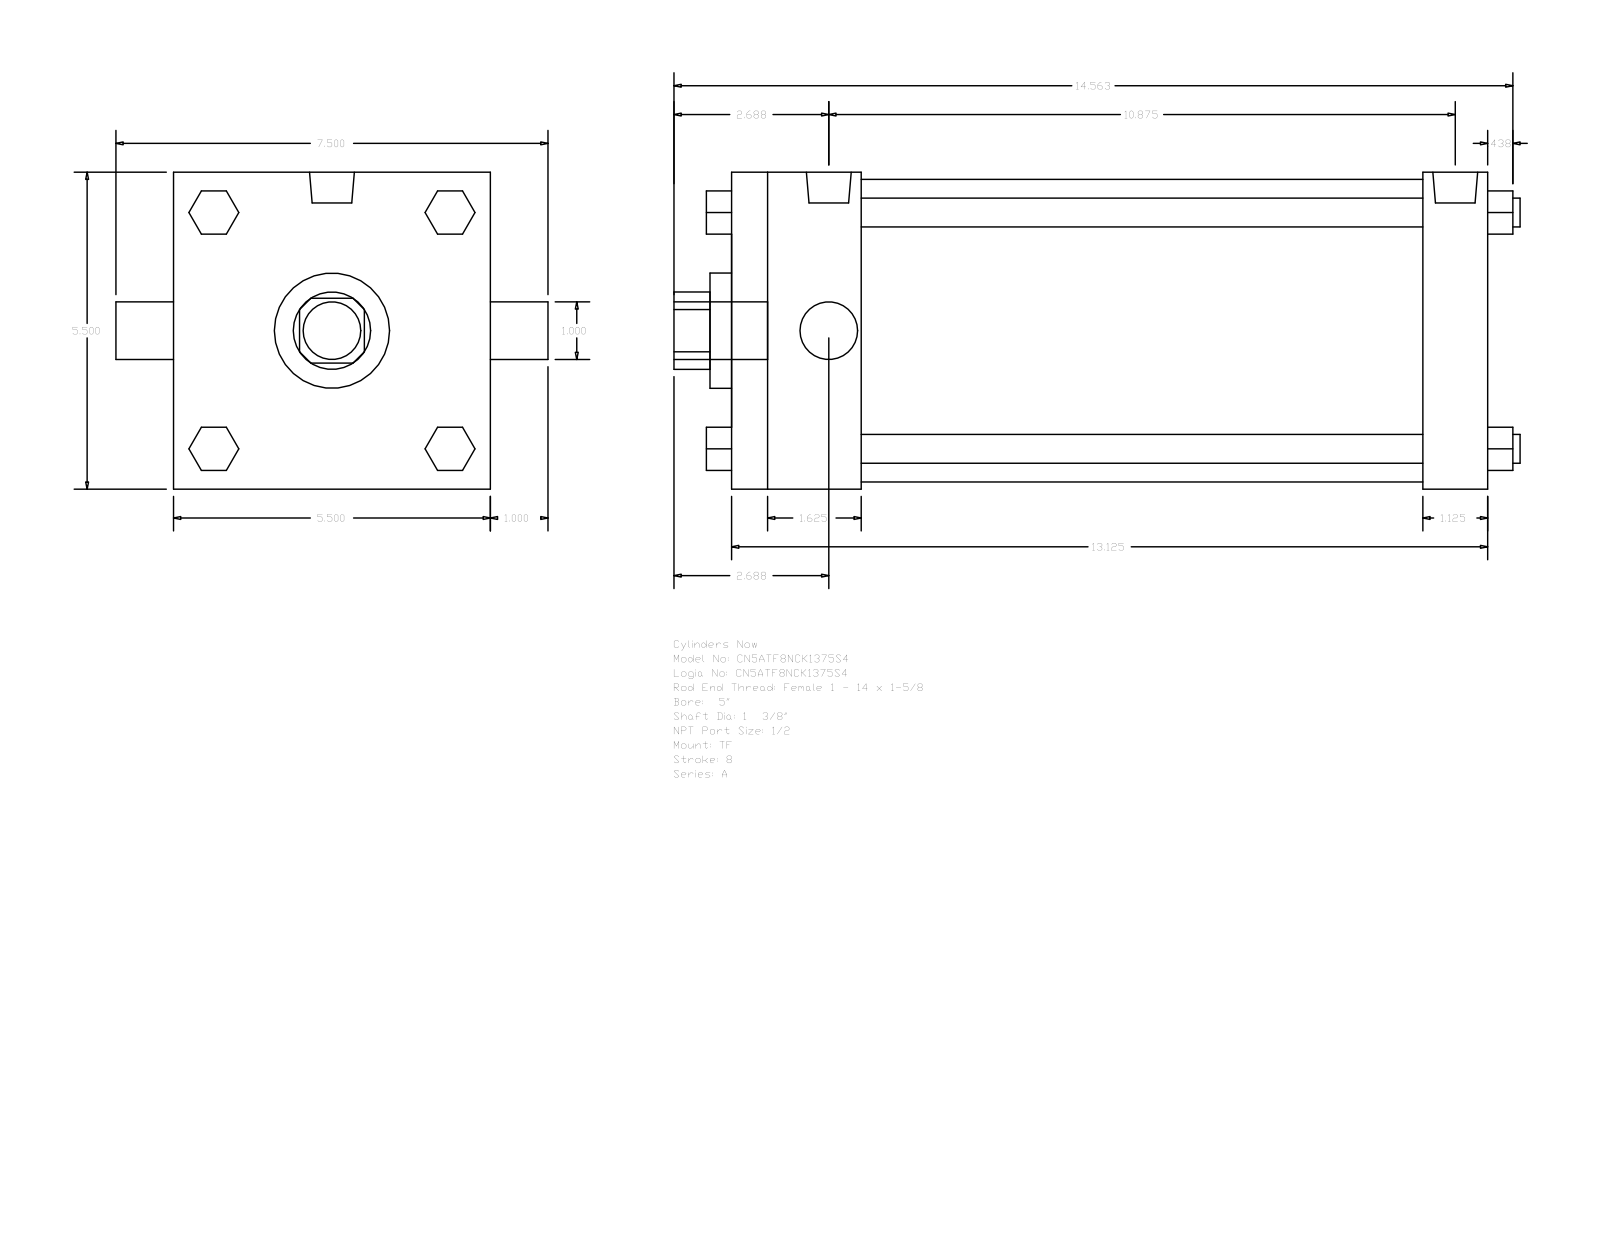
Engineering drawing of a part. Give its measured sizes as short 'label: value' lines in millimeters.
name: A_TF__0500_1.375
written by: GSSL Pune (CONFIG_CONTROL_DESIGN)
unit: mm
bodies: 0 solids, 120 faces (92 planar, 28 cylindrical, 0 other)
size: 373.06 × 190.5 × 139.7
holes: 1× ⌀25.4, 1× ⌀34.92, 1× ⌀50.8, 1× ⌀133.35
bosses: 4× ⌀12.7, 3× ⌀8.73, 2× ⌀19.77, 1× ⌀25.4
rounds: 1× R17.06
face distances: 139.7, 333.37, 28.57, 304.8, 57.15, 247.65, 276.22, 19.05, 52.07, 90.18
